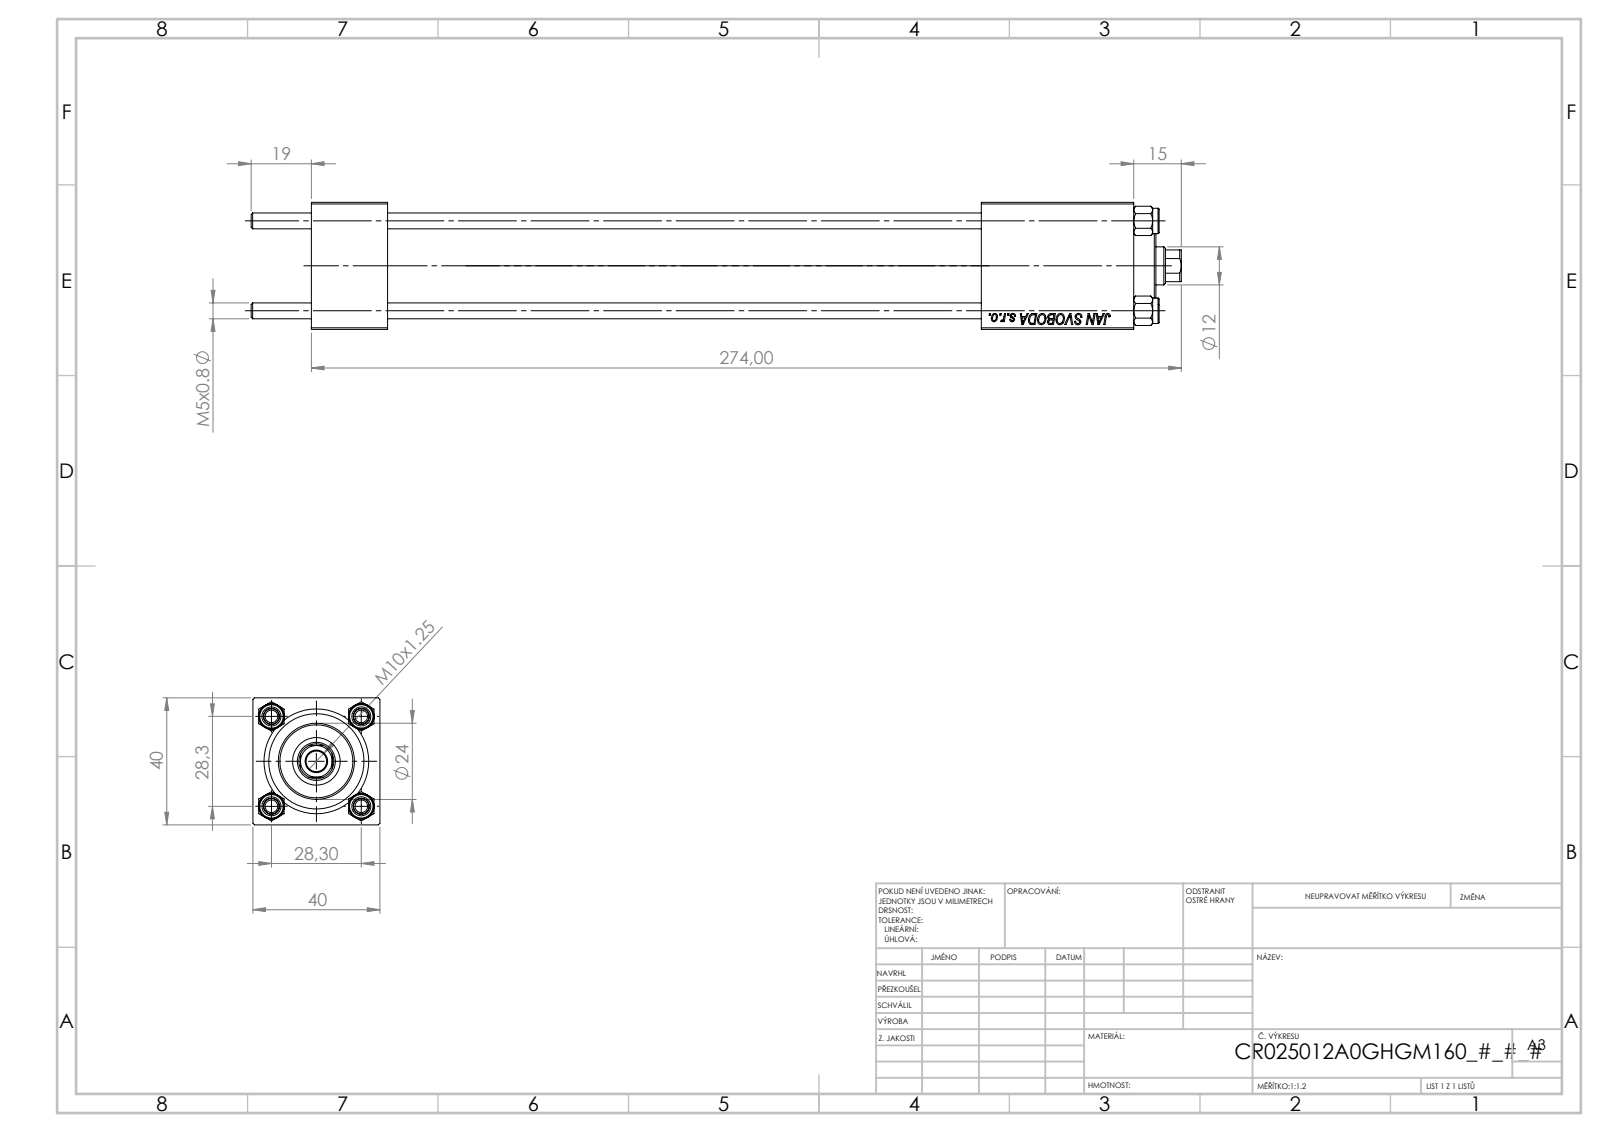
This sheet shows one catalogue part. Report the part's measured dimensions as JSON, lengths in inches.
{"part_name": "NUT_M5; V215CR_VCP; V215CR_BODY_A; V215_VC_A (+1 more)", "step_written_by": "SolidWorks 2019 (CONFIG_CONTROL_DESIGN)", "units": "inches", "bodies": {"solids": 11, "faces": 1131, "planar": 517, "cylindrical": 78, "other": 536}, "overall_size": [11.535, 1.575, 1.575], "volume_in3": 12.73, "surface_area_in2": 151.2, "round_holes": [[0.197, 4], [0.787, 3], [0.276, 2], [0.518, 2], [0.256, 1], [0.472, 1], [0.591, 1], [0.984, 1], [1.181, 1]], "round_bosses_or_shafts": [[0.315, 4], [1.22, 1], [0.945, 1]], "partial_cylinders_radius": [[0.217, 1]], "face_to_face_distances": [1.575, 0.945, 10.197, 9.252, 9.067, 8.122, 1.13, 8.307, 7.362, 0.76], "hole_center_spacings": [0.788, 1.114, 1.576, 8.346]}
